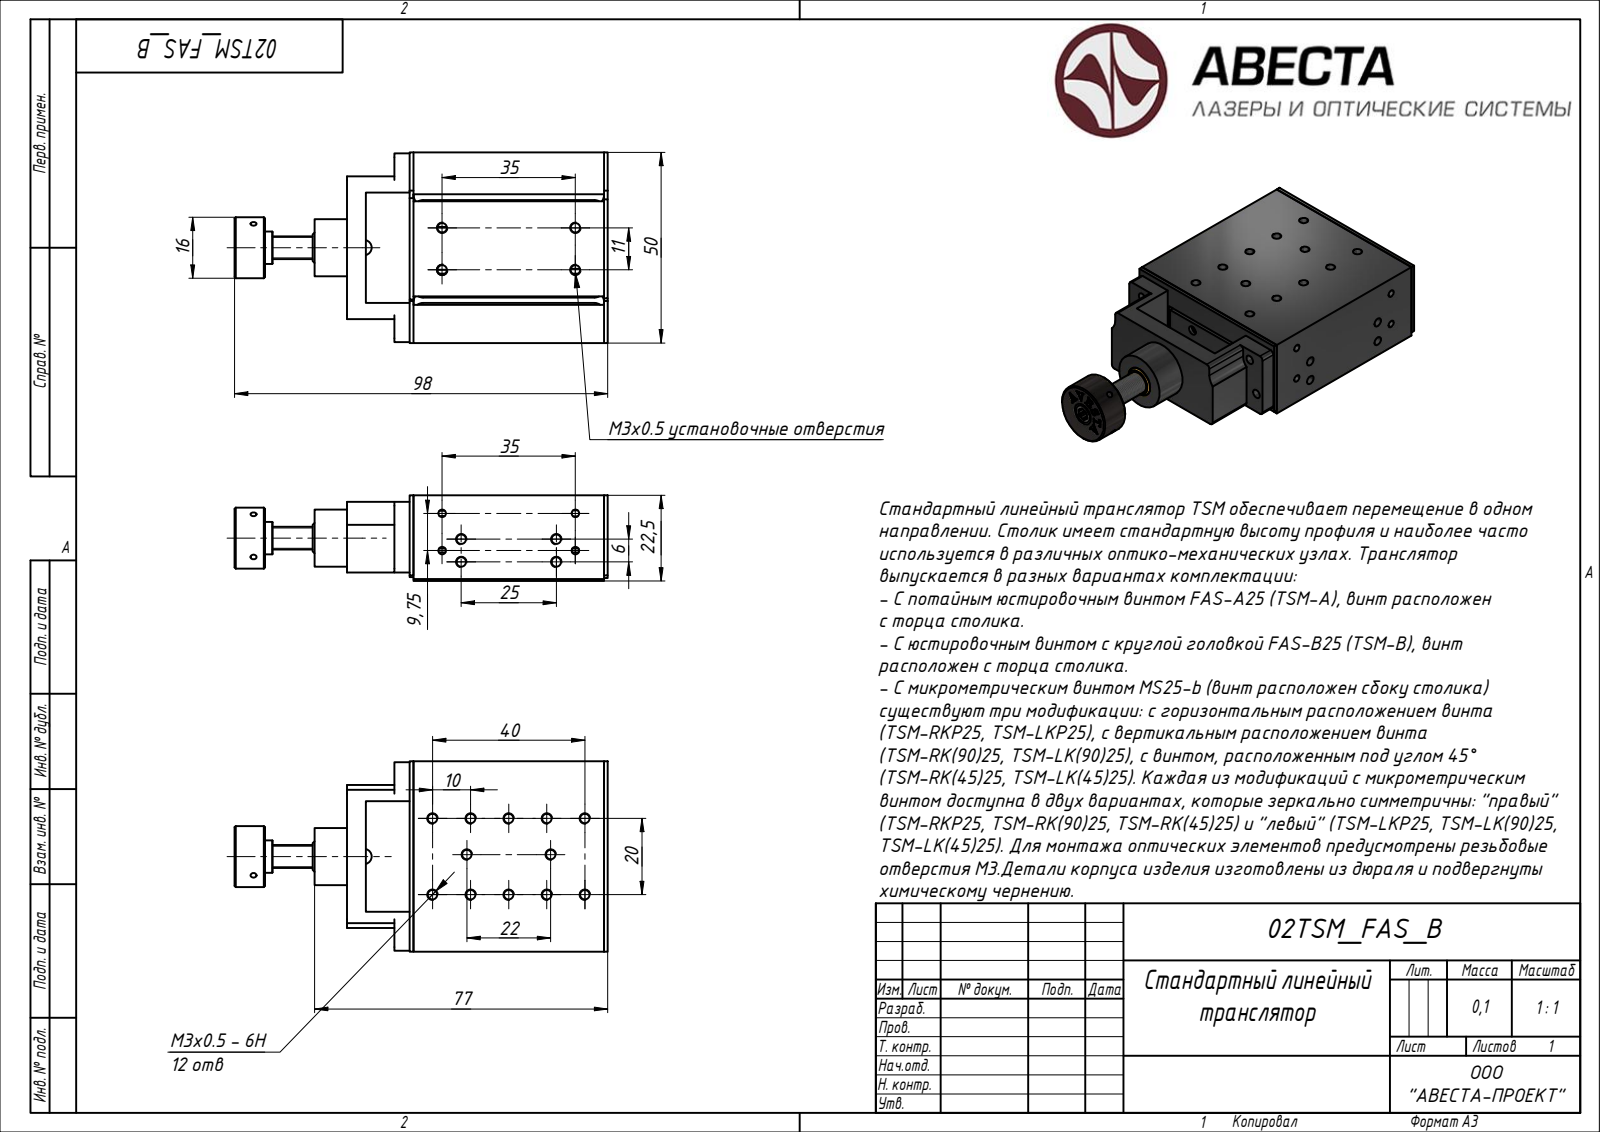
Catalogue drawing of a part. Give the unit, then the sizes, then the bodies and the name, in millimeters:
Units: millimetres
Overall size (bounding box): 90 × 50 × 22.5
Bodies: 10 solids, 654 faces (0 planar, 0 cylindrical, 654 other)
STEP written by: ST-DEVELOPER v15 (AUTOMOTIVE_DESIGN)
